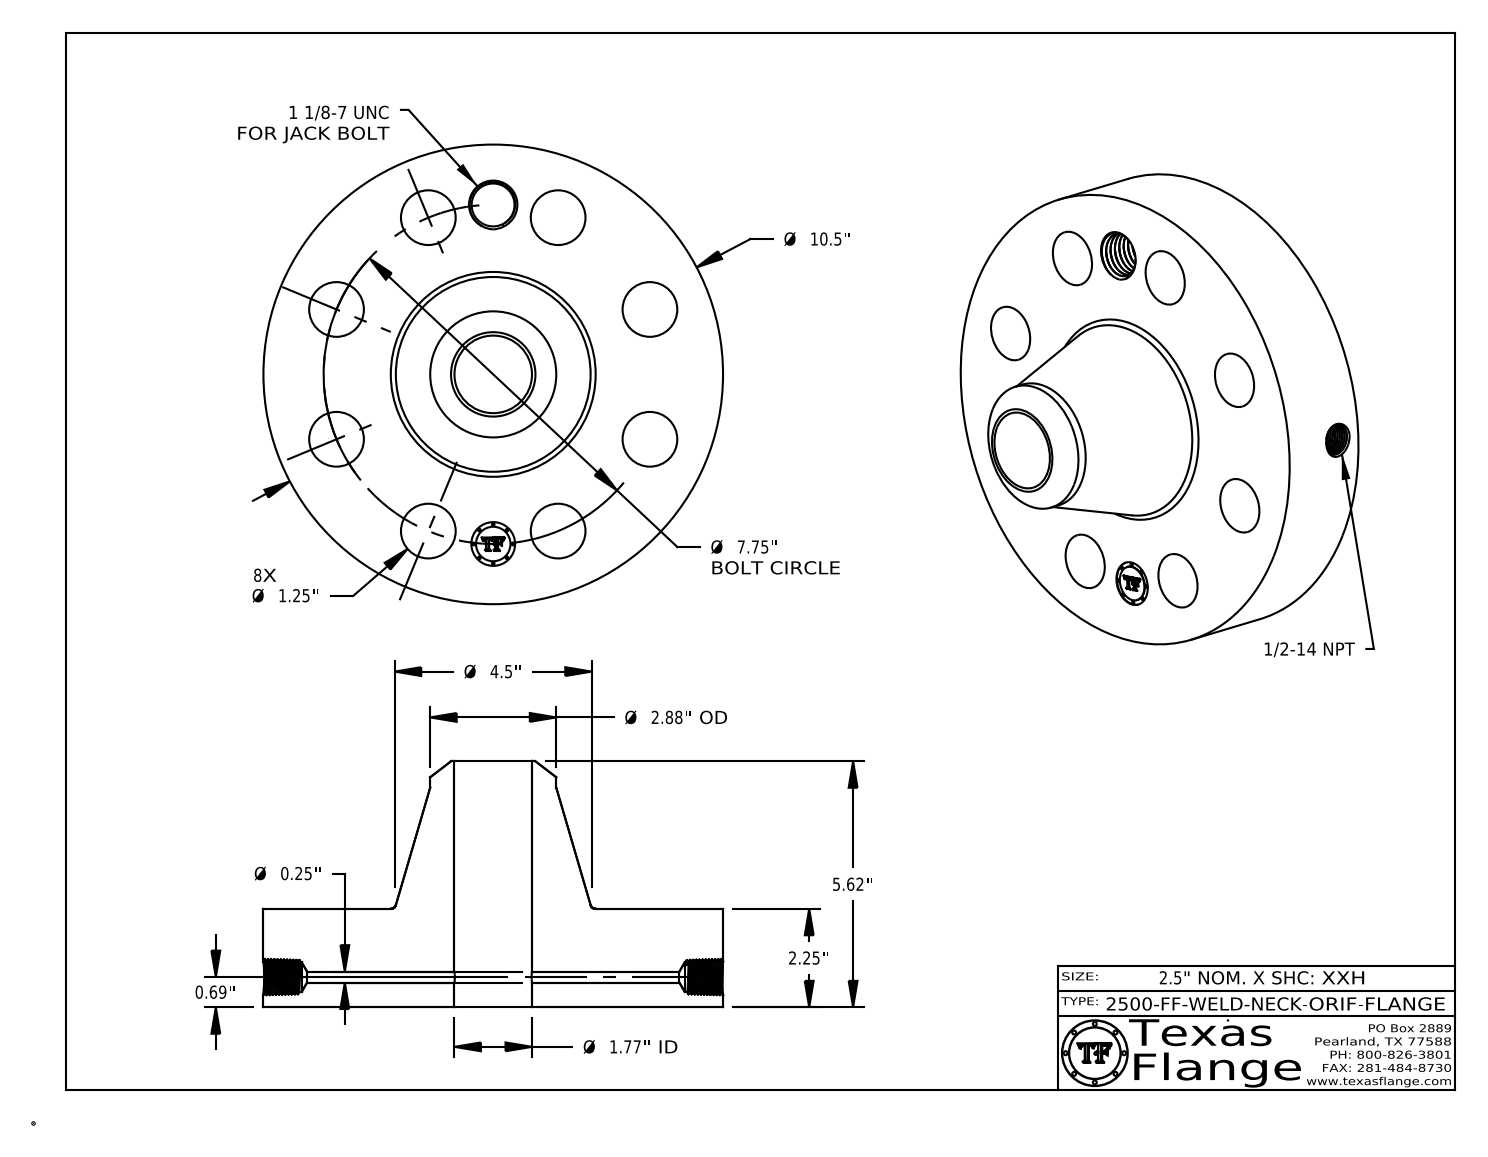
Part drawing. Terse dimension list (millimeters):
name: 2500-FF-WELD-NECK
written by: CATIA V5 STEP AP214 (AUTOMOTIVE_DESIGN)
unit: mm
bodies: 1 solid, 772 faces (368 planar, 93 cylindrical, 311 other)
size: 266.7 × 266.7 × 142.7
volume: 3 099 000 mm³; area: 240 300 mm²
holes: 8× ⌀31.8, 1× ⌀6.4, 1× ⌀17.1, 1× ⌀25, 1× ⌀25.4, 1× ⌀45
bosses: 8× ⌀1.5, 1× ⌀266.7, 1× ⌀73.2, 1× ⌀20
face distances: 57.2, 142.7, 85.6, 0.4, 56.8, 86, 7.6, 7.4, 1.4, 6.3
hole spacings: 98.4, 139.2, 38.4, 75.3, 75.3, 109.4, 163.7, 181.9
